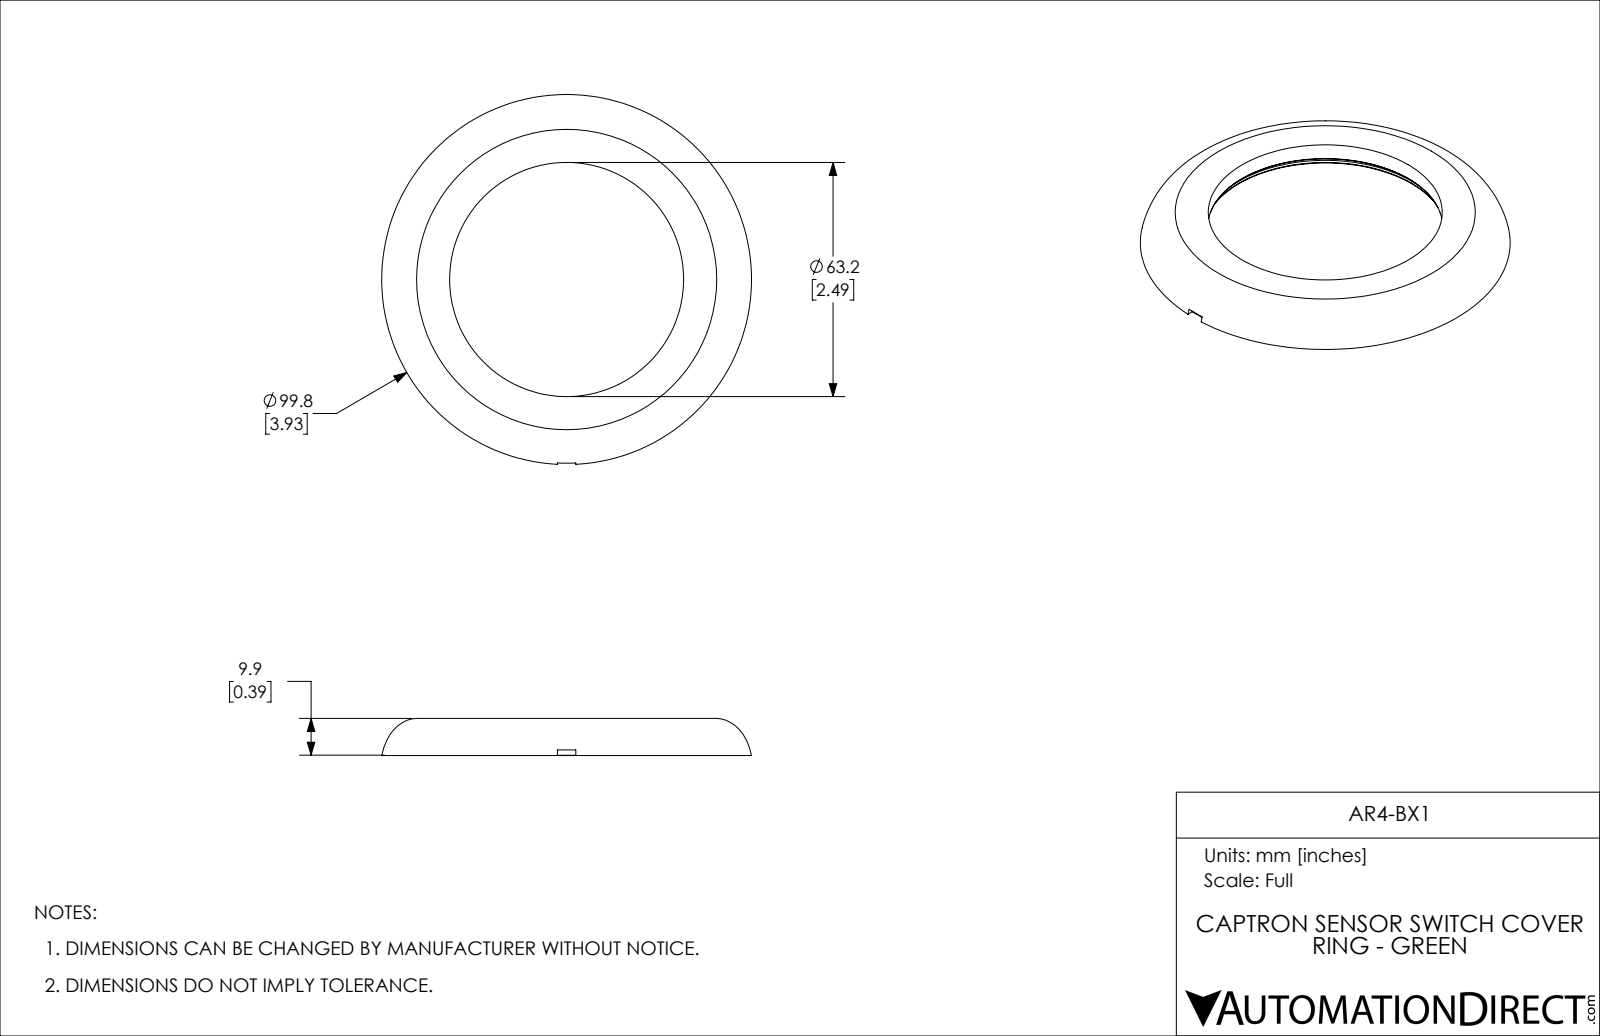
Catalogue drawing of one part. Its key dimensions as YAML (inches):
part_name: "AR4-BX1"
step_written_by: "SolidWorks 2019 (CONFIG_CONTROL_DESIGN)"
units: inches
bodies: {solids: 1, faces: 49, planar: 7, cylindrical: 4, other: 38}
overall_size: [3.929, 3.927, 0.394]
volume: 0.743
surface_area: 22.88
round_holes:
  - {diameter: 2.583, count: 1}
  - {diameter: 3.714, count: 1}
face_to_face_distances: [0.079, 0.197, 0.276, 0.087, 0.11, 0.189, 0.059, 0.146, 0.256, 0.335]
